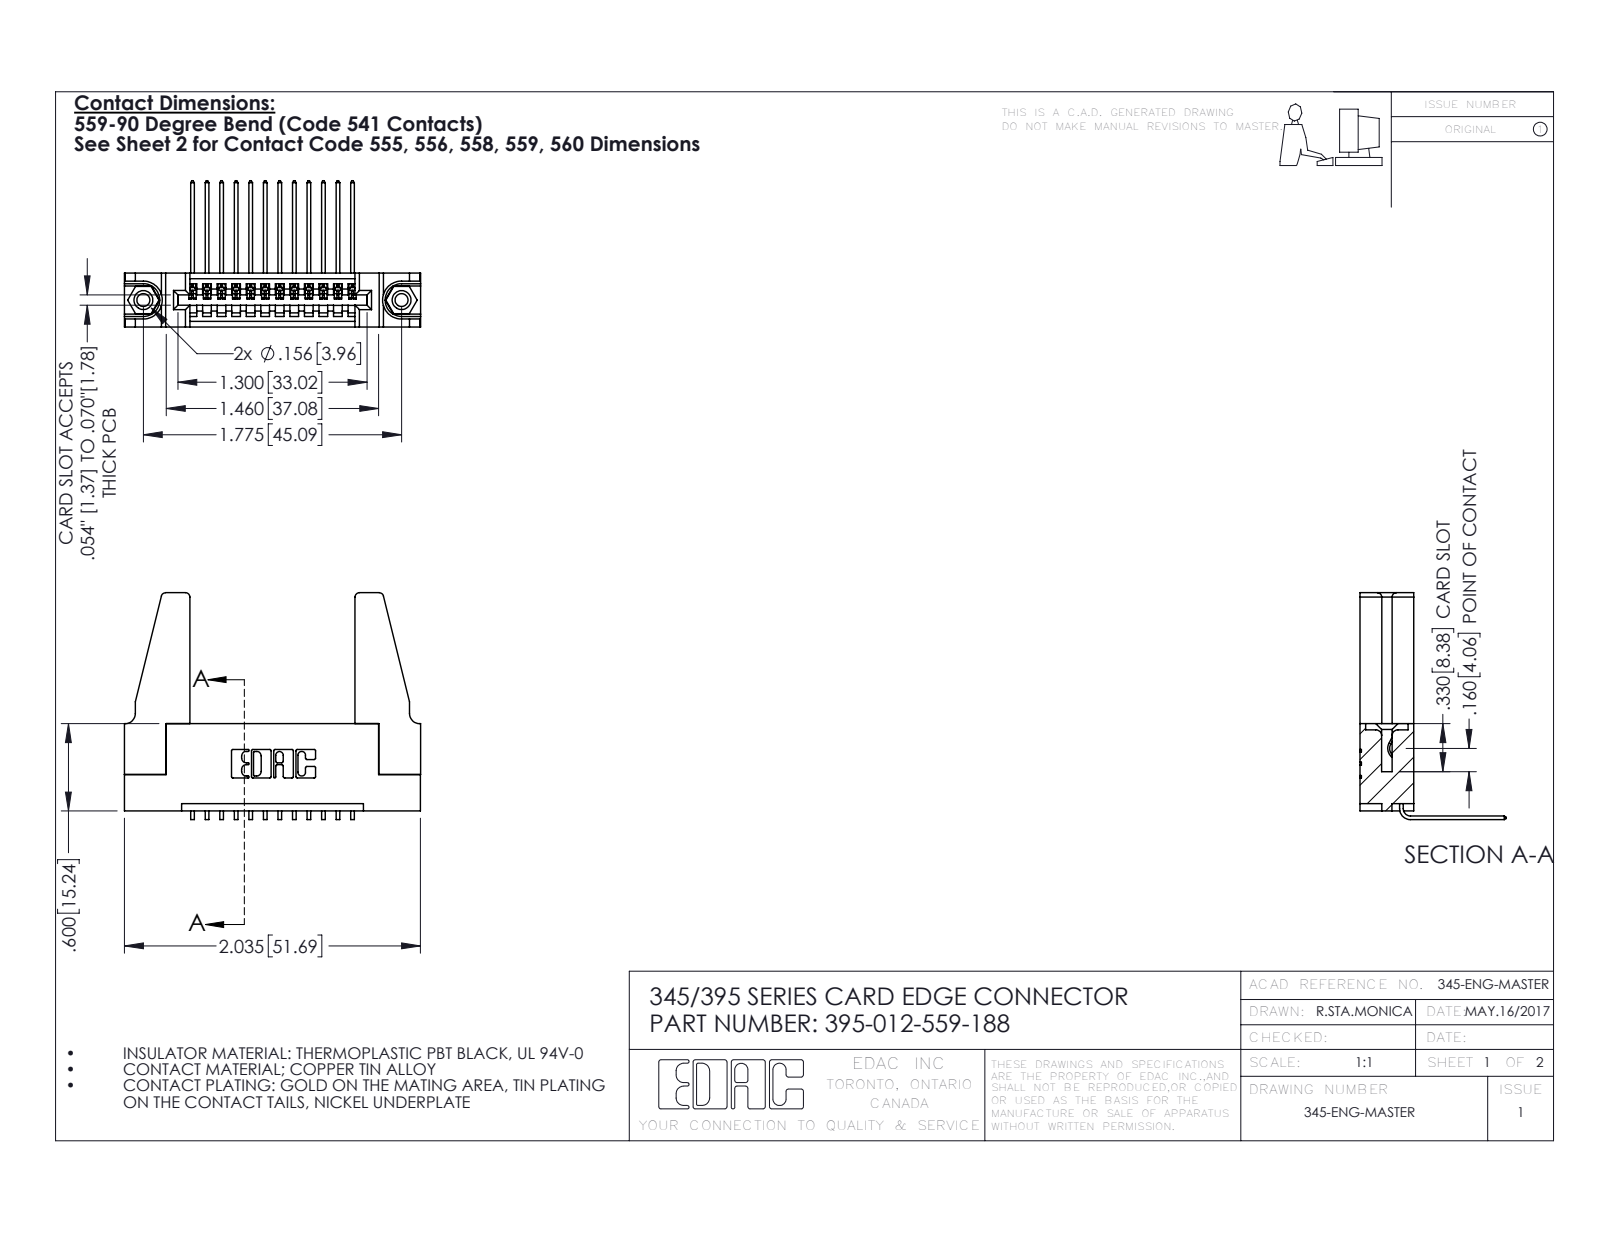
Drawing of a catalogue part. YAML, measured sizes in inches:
part_name: "345-250-001_345-250-001-102; 395-012-559-188; 345-220-078_345-220-088; 345-292-001_558 559 Tail - 1 (+1 more)"
step_written_by: "SolidWorks 2016 (CONFIG_CONTROL_DESIGN)"
units: inches
bodies: {solids: 17, faces: 970, planar: 656, cylindrical: 298, other: 16}
overall_size: [2.036, 1.559, 1.005]
volume: 0.486
surface_area: 14.28
round_holes:
  - {diameter: 0.089, count: 2}
  - {diameter: 0.125, count: 2}
  - {diameter: 0.156, count: 2}
  - {diameter: 0.064, count: 1}
round_bosses_or_shafts:
  - {diameter: 0.155, count: 2}
partial_cylinders:
  - {radius: 0.006, count: 24}
  - {radius: 0.01, count: 22}
  - {radius: 0.03, count: 8}
  - {radius: 0.007, count: 6}
  - {radius: 0.031, count: 6}
  - {radius: 0.026, count: 3}
  - {radius: 0.031, count: 2}
  - {radius: 0.04, count: 2}
face_to_face_distances: [0.37, 0.072, 0.298, 0.2, 0.098, 0.272, 0.025, 0.225, 0.148, 0.15]
hole_center_spacings: [0.27, 1.543, 1.775]
